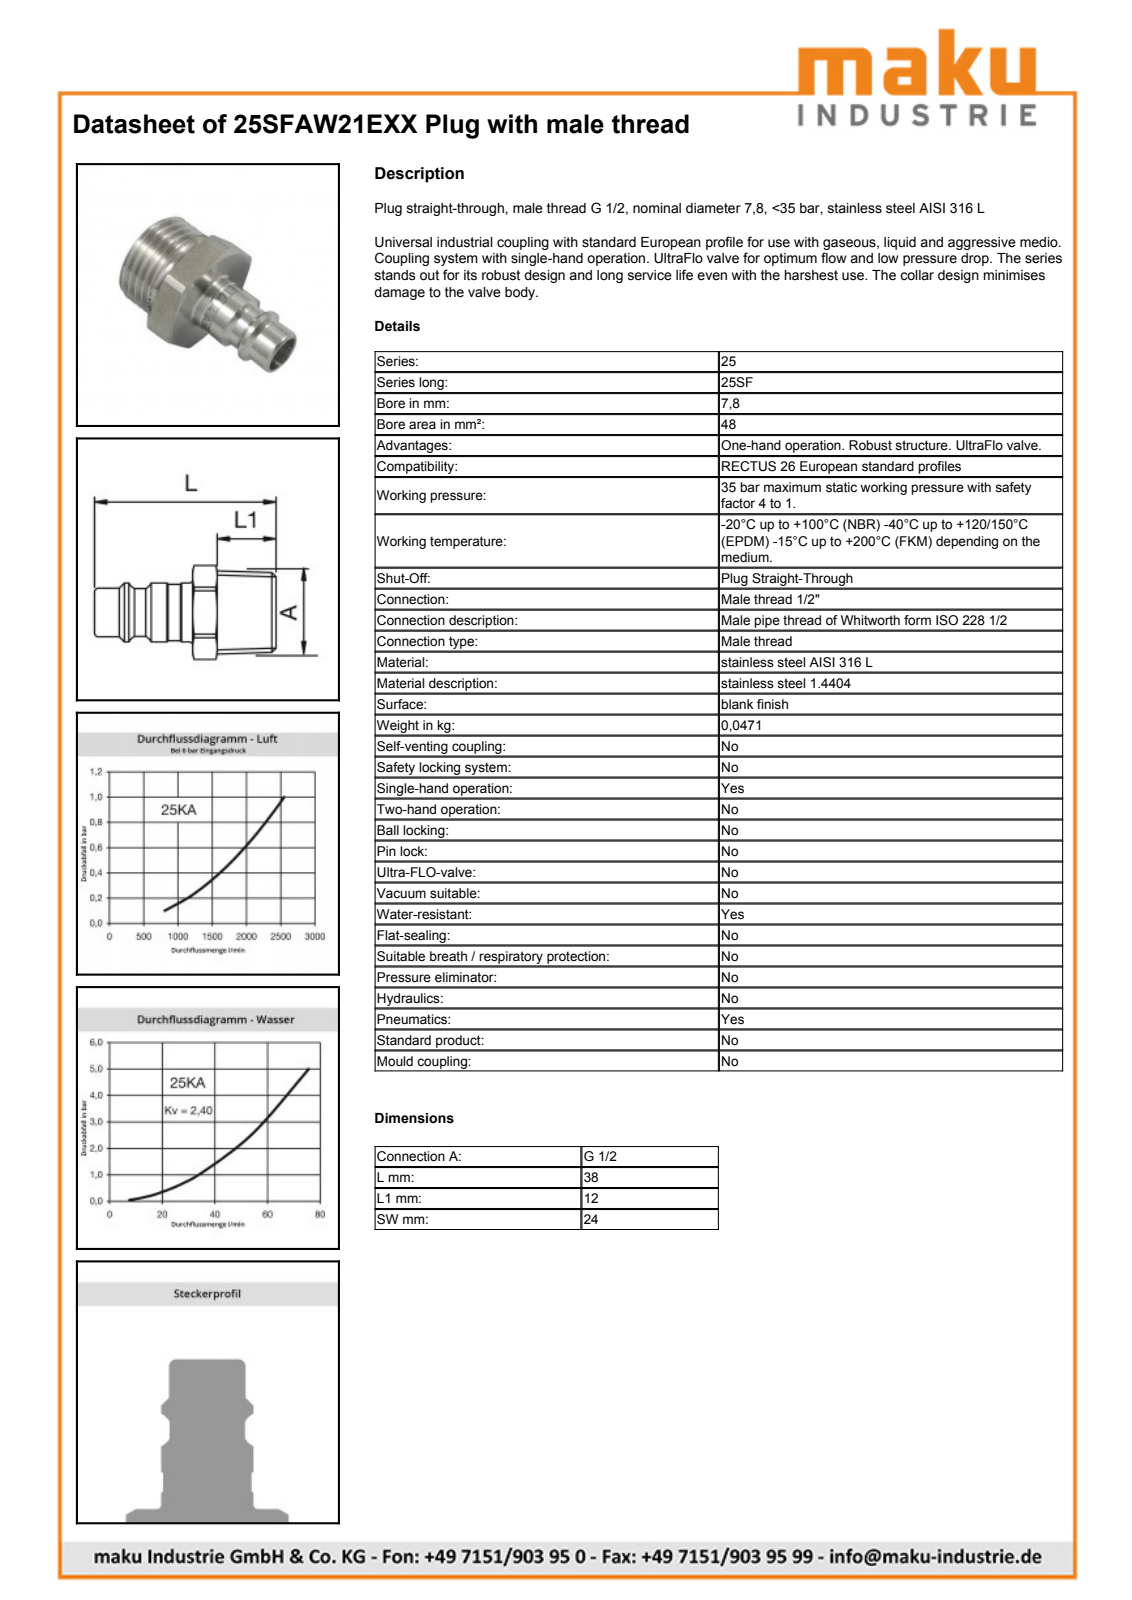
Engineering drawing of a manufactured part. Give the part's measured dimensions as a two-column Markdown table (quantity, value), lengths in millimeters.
| quantity | value |
| --- | --- |
| part name | D104286 |
| STEP written by | Autodesk Inventor 2013 (AUTOMOTIVE_DESIGN) |
| units | millimeters |
| bodies | 1 solid, 295 faces (109 planar, 33 cylindrical, 153 other) |
| overall size | 38 × 27.05 × 24 |
| volume | 6 323 mm³ |
| surface area | 3 784 mm² |
| round holes (diameter × count) | 7.85 × 1 |
| round bosses / shafts (diameter × count) | 20.95 × 1, 12 × 1, 11.5 × 1, 9.9 × 1, 9.75 × 1 |
| partial cylindrical surfaces (radius × count) | 5.65 × 1, 13.53 × 1 |
| main face-to-face distances | 24, 6, 18, 12, 20, 26, 38, 17.23, 2.77, 8.77 |
